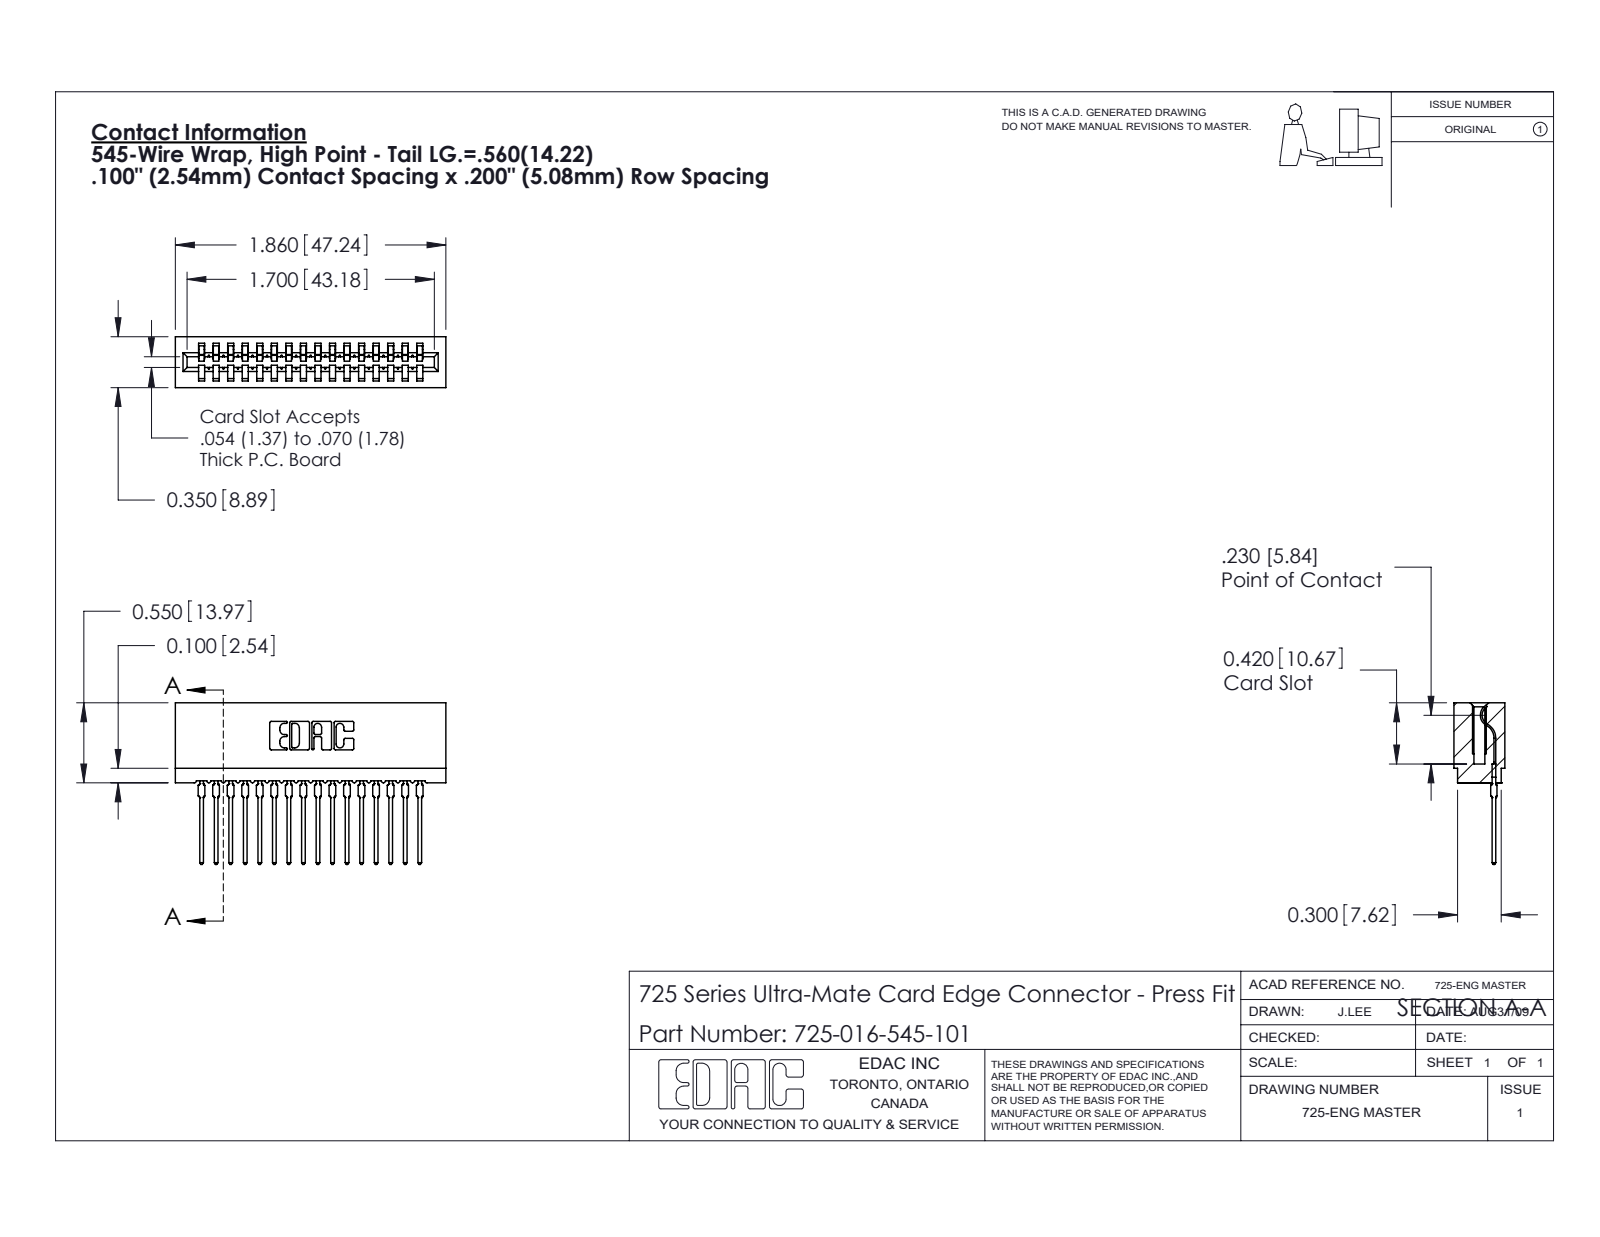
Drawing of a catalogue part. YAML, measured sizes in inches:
part_name: "725 Part_Insulator Option - 01; 745-292-001_545; 725-016-545-101"
step_written_by: "SolidWorks 2020 (CONFIG_CONTROL_DESIGN)"
units: inches
bodies: {solids: 17, faces: 1887, planar: 1127, cylindrical: 344, other: 416}
overall_size: [1.86, 1.111, 0.35]
volume: 0.23
surface_area: 10.9
partial_cylinders:
  - {radius: 0.015, count: 32}
  - {radius: 0.021, count: 32}
  - {radius: 0.01, count: 22}
  - {radius: 0.007, count: 6}
  - {radius: 0.031, count: 6}
  - {radius: 0.005, count: 4}
  - {radius: 0.011, count: 4}
  - {radius: 0.026, count: 3}
face_to_face_distances: [0.1, 0.2, 0.3, 0.4, 0.5, 0.6, 0.7, 0.35, 0.212, 0.138]
